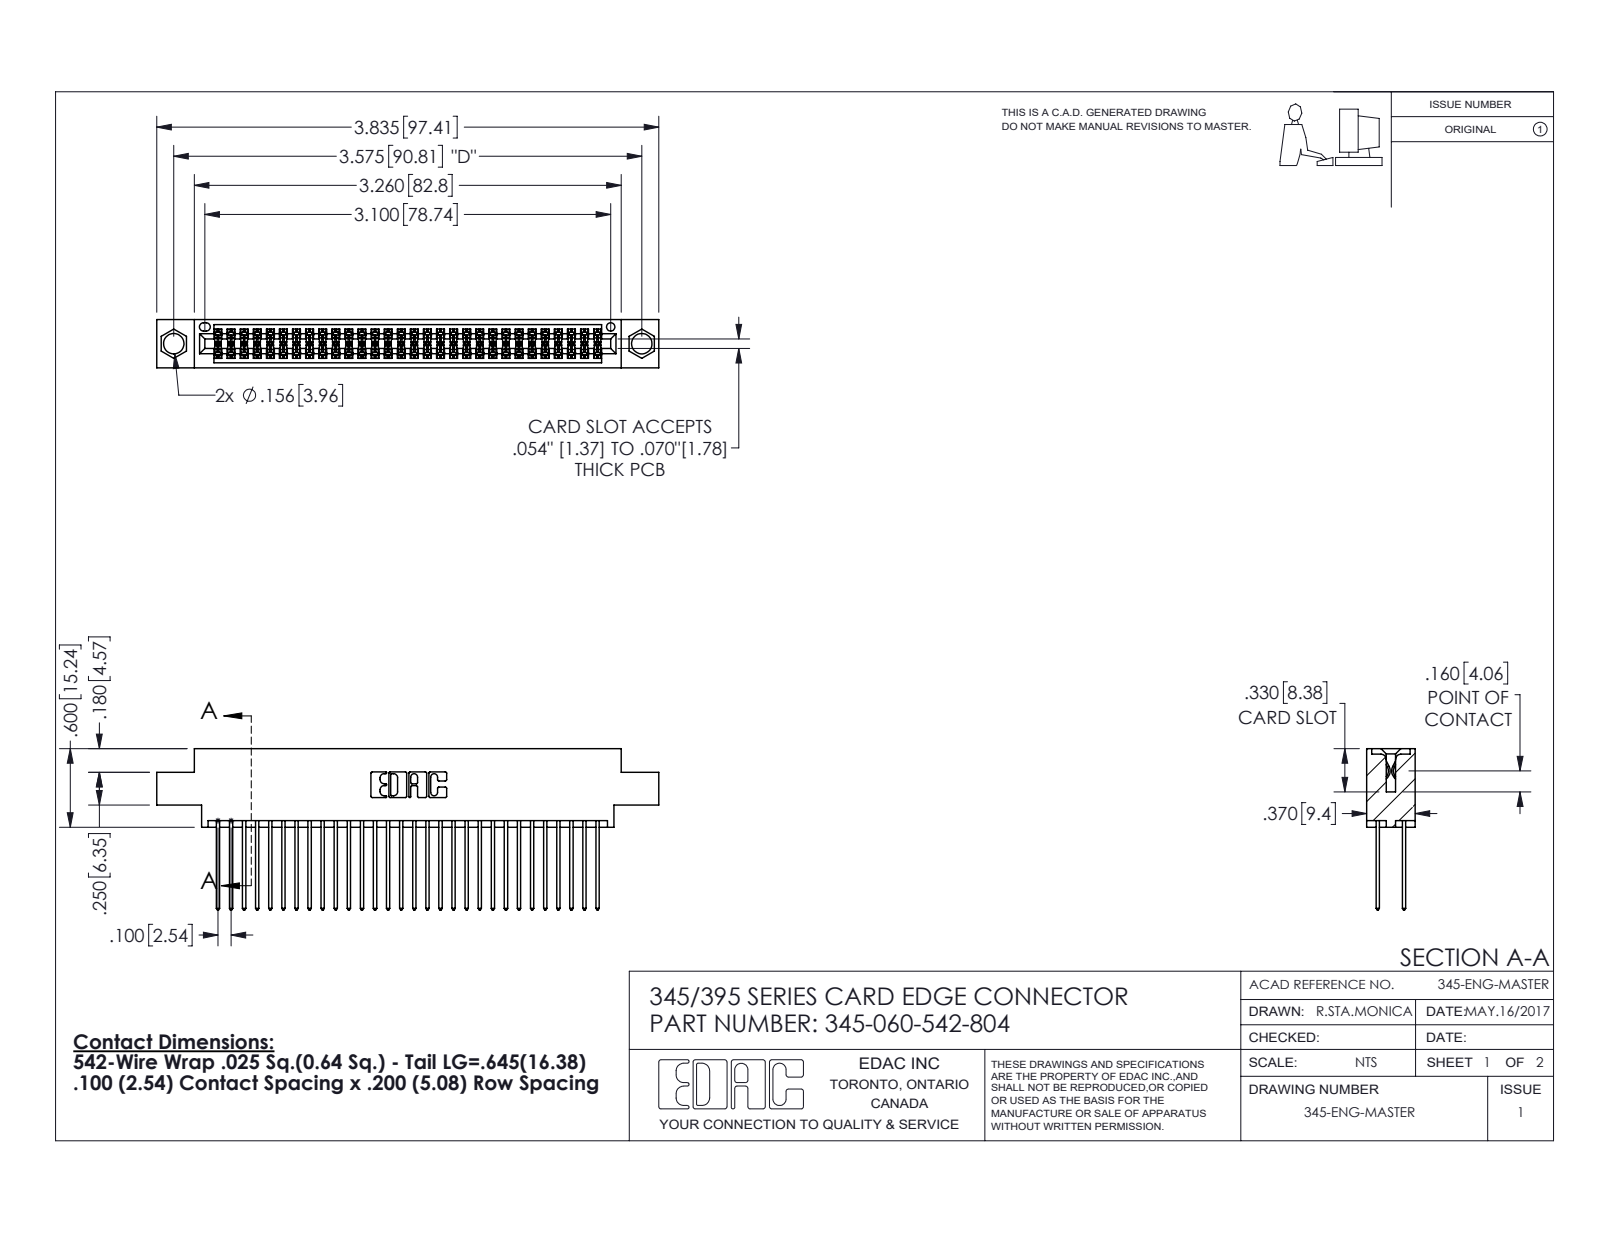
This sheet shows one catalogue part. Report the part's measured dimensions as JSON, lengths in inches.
{"part_name": "345 Part_0.170 Offset - 0.156 Dia-TI; 345-060-542-804; 345-292-001_345-293-142", "step_written_by": "SolidWorks 2020 (CONFIG_CONTROL_DESIGN)", "units": "inches", "bodies": {"solids": 61, "faces": 3144, "planar": 2078, "cylindrical": 1066, "other": 0}, "overall_size": [3.835, 1.232, 0.37], "volume_in3": 0.574, "surface_area_in2": 23.22, "round_holes": [[0.156, 2], [0.064, 1]], "partial_cylinders_radius": [[0.006, 120], [0.01, 60], [0.01, 22], [0.007, 6], [0.031, 6], [0.026, 3], [0.014, 2], [0.019, 2]], "face_to_face_distances": [0.072, 0.298, 0.2, 0.098, 0.272, 0.025, 0.37, 0.225, 0.175, 0.149], "hole_center_spacings": [0.27, 3.34, 3.575]}
